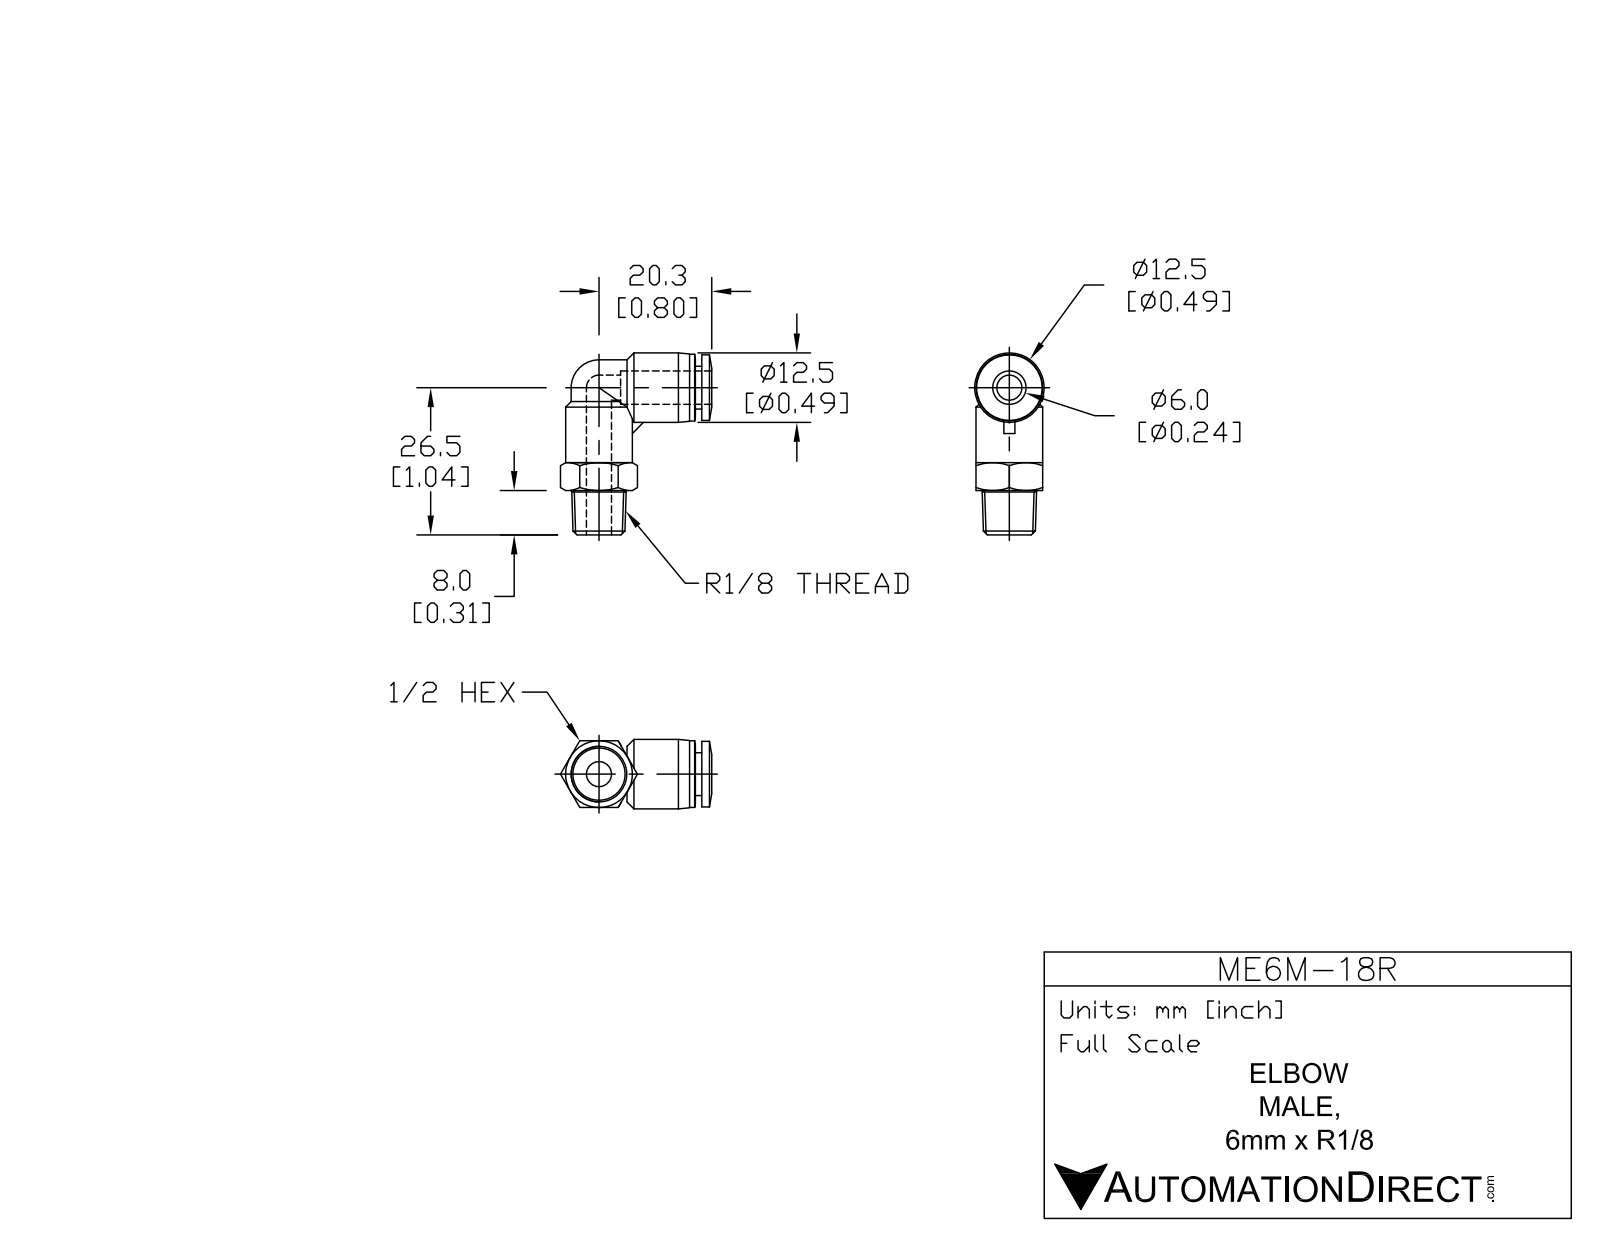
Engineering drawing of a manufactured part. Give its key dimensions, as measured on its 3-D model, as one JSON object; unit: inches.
{"part_name": "ME6M-18R", "step_written_by": "SolidWorks 2015 (AUTOMOTIVE_DESIGN)", "units": "inches", "bodies": {"solids": 1, "faces": 66, "planar": 16, "cylindrical": 19, "other": 31}, "overall_size": [1.289, 1.072, 0.492], "volume_in3": 0.23, "surface_area_in2": 4.125, "round_holes": [[0.157, 2], [0.248, 1]], "round_bosses_or_shafts": [[0.472, 2], [0.492, 1], [0.465, 1], [0.303, 1]], "partial_cylinders_radius": [[0.197, 2]], "face_to_face_distances": [0.472, 0.045, 0.315, 0.53, 0.575, 0.197, 0.276, 0.646, 0.116, 0.071]}
